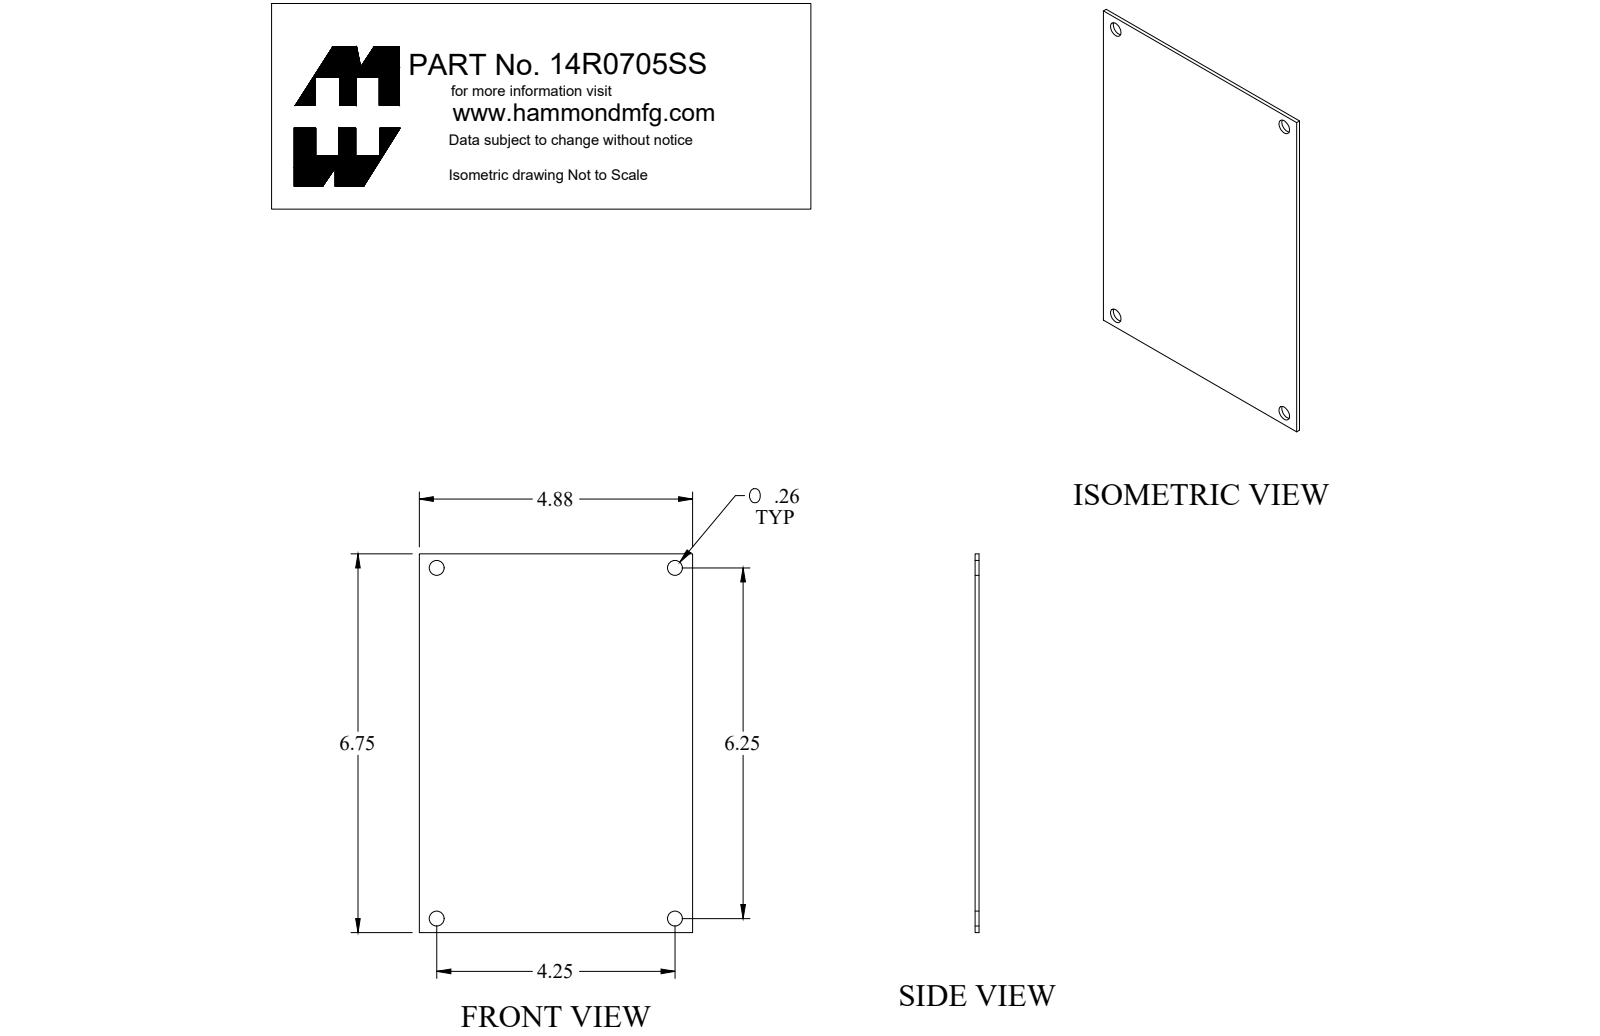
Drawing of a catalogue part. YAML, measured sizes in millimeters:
part_name: "14R0705SS"
step_written_by: "SolidWorks 2018 (AUTOMOTIVE_DESIGN)"
units: millimeters
bodies: {solids: 1, faces: 10, planar: 6, cylindrical: 4, other: 0}
overall_size: [171.5, 123.8, 1.8]
volume: 38560
surface_area: 43410
round_holes:
  - {diameter: 6.7, count: 4}
face_to_face_distances: [1.8, 123.8, 171.5]
hole_center_spacings: [108, 158.8, 192]
